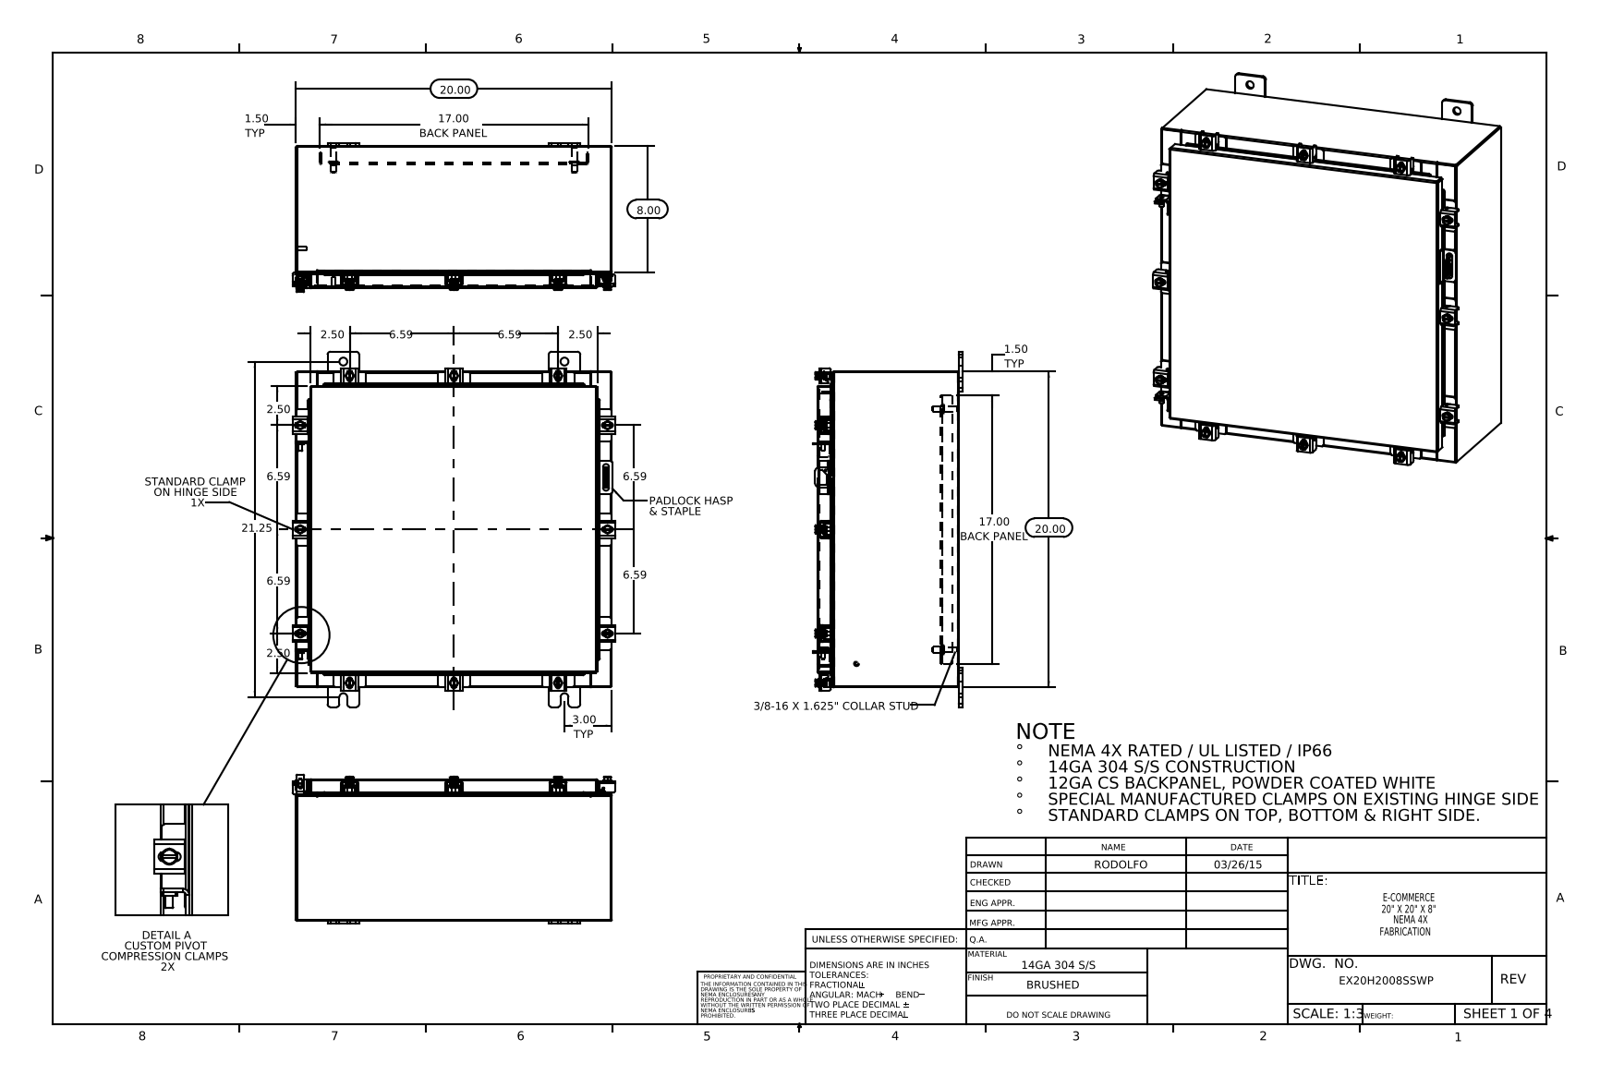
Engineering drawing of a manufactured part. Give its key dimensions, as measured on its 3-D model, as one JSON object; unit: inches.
{"part_name": "EX20H2008SSWP Top; EX20H2008SSWP Cover; 30X10 Clamp Bracket2; Special Clamp Assembly (+8 more)", "step_written_by": "SolidWorks 2014 (CONFIG_CONTROL_DESIGN)", "units": "inches", "bodies": {"solids": 81, "faces": 2018, "planar": 1075, "cylindrical": 783, "other": 160}, "overall_size": [22.5, 20.421, 9.453], "volume_in3": 161.6, "surface_area_in2": 4054, "round_holes": [[0.213, 12], [0.26, 12], [0.5, 8], [0.125, 1], [0.25, 1]], "round_bosses_or_shafts": [[0.5, 12], [0.25, 12], [0.399, 10], [0.625, 4], [0.375, 4], [0.33, 4], [0.315, 2], [0.236, 2]], "partial_cylinders_radius": [[0.06, 54], [0.013, 24], [0.141, 24], [0.19, 24], [0.088, 22], [0.12, 22], [0.09, 18], [0.05, 17]], "face_to_face_distances": [0.075, 8.9, 19.925, 8.975, 8.826, 19.85, 20, 0.104, 1, 1.075], "hole_center_spacings": [6.594, 10.217, 16.617, 18.998, 20.539, 2.34, 14.374, 17.381]}
